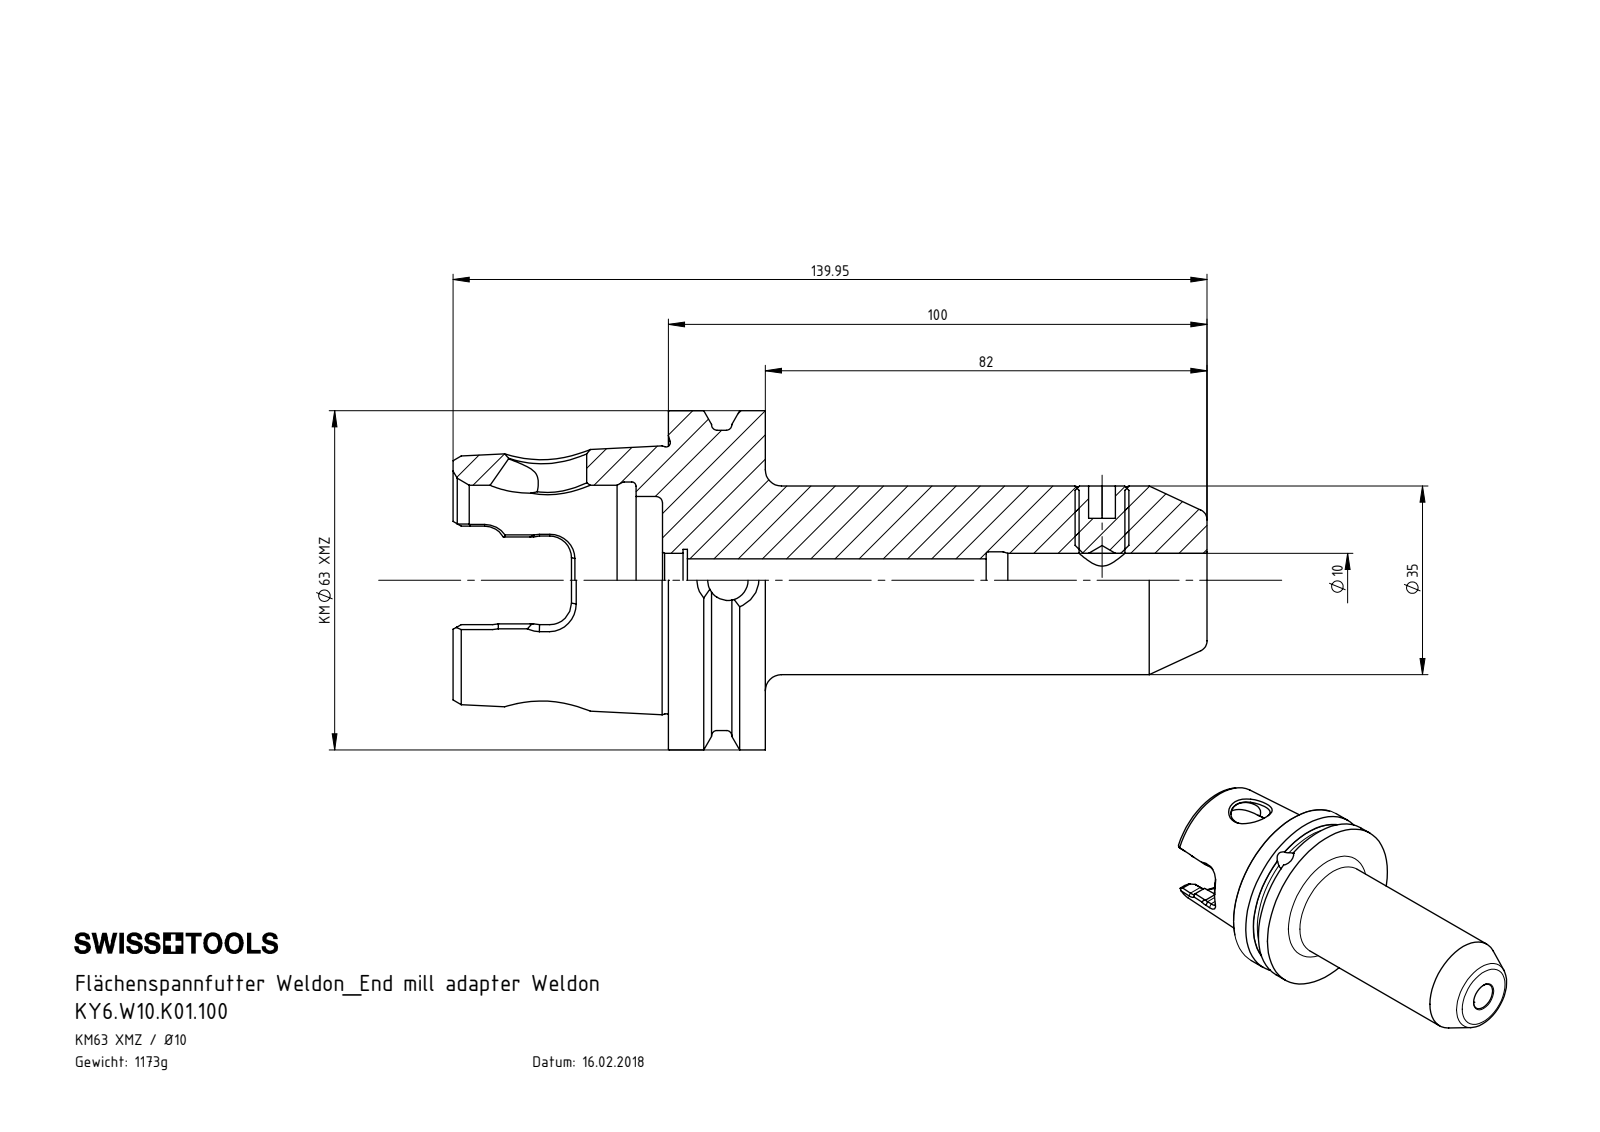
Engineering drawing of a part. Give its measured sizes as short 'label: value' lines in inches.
name: W10-ER1.001.012; KY6.W10.K01.100; KY6-W10.K01.100_A
written by: SolidWorks 2017 (CONFIG_CONTROL_DESIGN)
unit: in
bodies: 2 solids, 242 faces (55 planar, 56 cylindrical, 131 other)
size: 5.51 × 2.478 × 2.478
volume: 9.114 in³; area: 49.03 in²
holes: 2× ⌀0.294, 1× ⌀0.315, 1× ⌀0.334, 1× ⌀0.335, 1× ⌀0.394, 1× ⌀0.417, 1× ⌀0.453, 1× ⌀0.571, 1× ⌀1.224, 1× ⌀1.389, 1× ⌀1.437
bosses: 1× ⌀2.478, 1× ⌀2.193, 1× ⌀1.378, 1× ⌀0.394
rounds: 6× R0.157, 2× R0.277
face distances: 0.709, 0.043, 0.752, 3.98, 3.937, 3.228, 0.236, 0.945, 0.193, 4.173
hole spacings: 4.051
